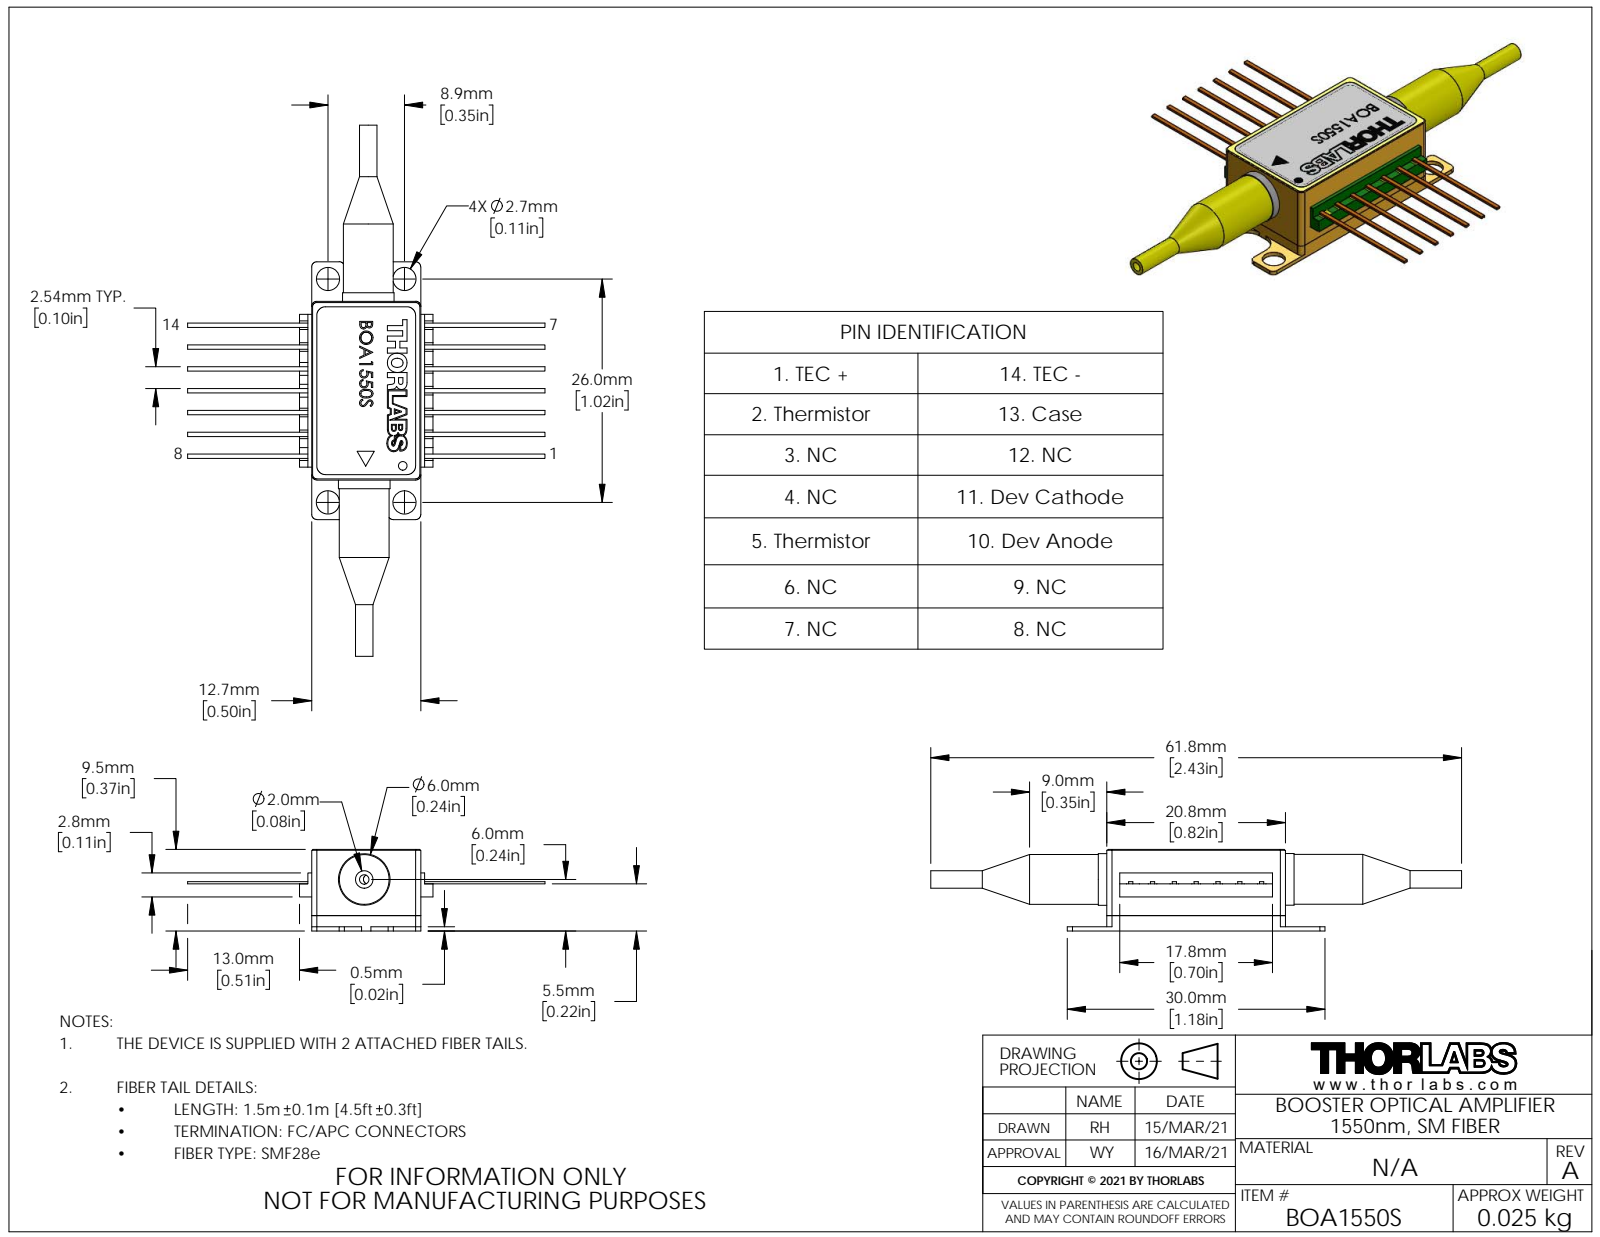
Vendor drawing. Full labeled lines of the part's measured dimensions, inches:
Part name (STEP PRODUCT): QTN042067-E0W
STEP written by: SolidWorks 2018 (AUTOMOTIVE_DESIGN)
Units: inches
Bodies: 0 solids, 358 faces (252 planar, 54 cylindrical, 52 other)
Overall size (bounding box): 2.433 × 1.638 × 0.374
Round holes (diameter × count): ⌀0.106 ×4, ⌀0.043 ×2, ⌀0.039 ×1
Round bosses / shafts (diameter × count): ⌀0.236 ×2, ⌀0.228 ×2, ⌀0.08 ×2
Partial cylindrical surfaces — rounded edges, fillets, slot ends (radius × count): R0.024 ×12, R0.02 ×4, R0.039 ×4, R0.079 ×4
Main face-to-face distances: 0.373, 0.5, 0.156, 0.217, 0.217, 0.06, 0.157, 0.02, 0.07, 0.226
Hole centre spacings: 0.35, 1.024, 1.082, 0.018, 0.168, 0.381, 0.856, 0.922
